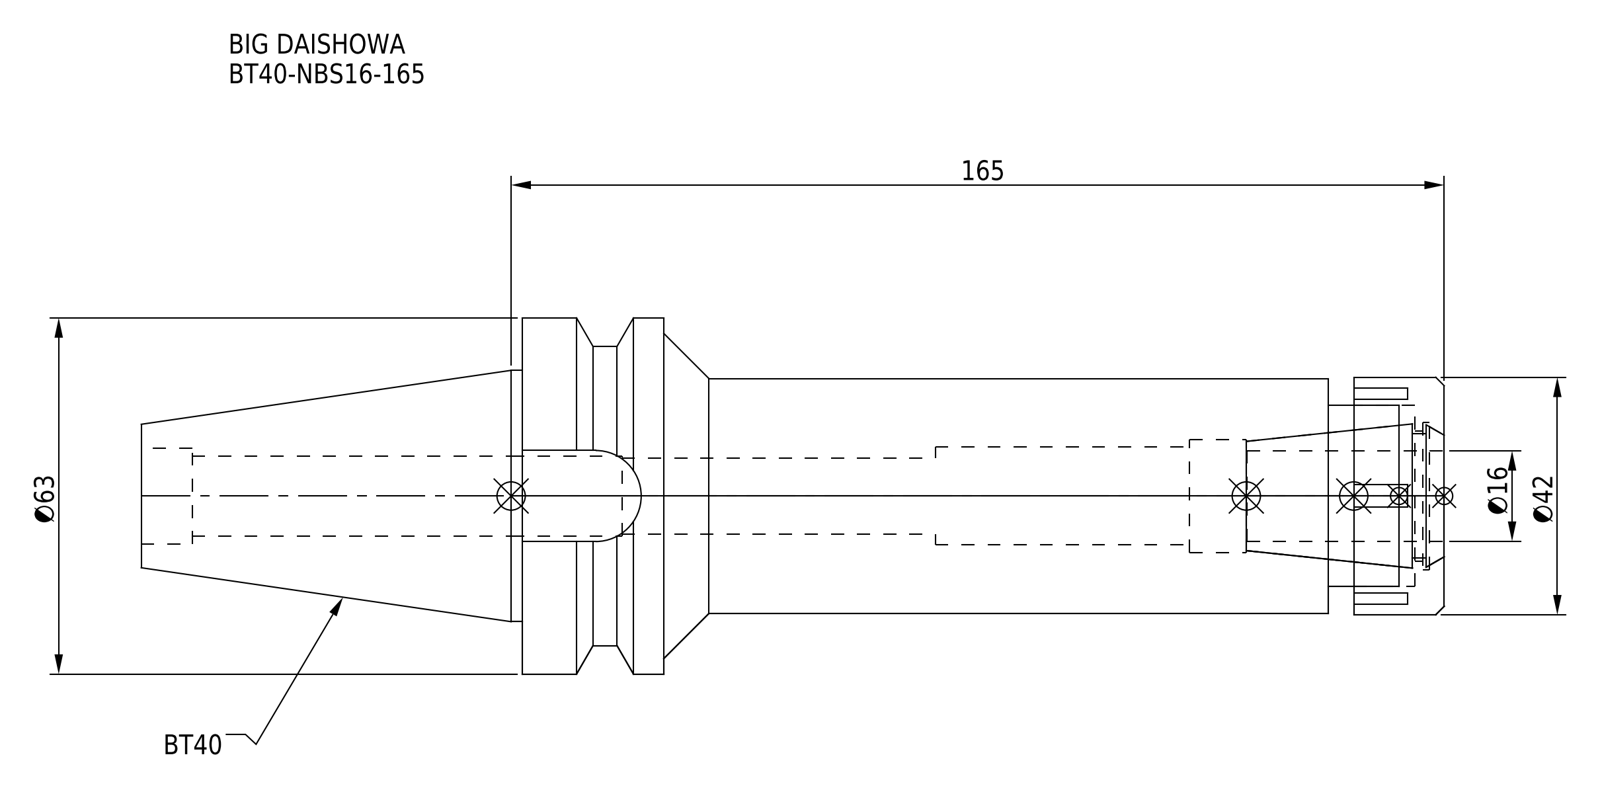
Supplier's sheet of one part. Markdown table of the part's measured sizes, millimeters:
| quantity | value |
| --- | --- |
| part name | DXF_TEMP_ASSY_ASM_4_ASM.stp; BT40-NBS16-165.stp; BT40-NBS16-165; BT40NB16165-160_ASM.stp (+3 more) |
| STEP written by | SolidWorks 2019 (CONFIG_CONTROL_DESIGN) |
| units | millimeters |
| bodies | 2 solids, 93 faces (45 planar, 34 cylindrical, 14 other) |
| overall size | 230.4 × 63 × 63 |
| volume | 272 263 mm³ |
| surface area | 51 448 mm² |
| round holes (diameter × count) | 13.5 × 1, 14.2 × 1, 17 × 1, 17.3 × 1, 20 × 1, 23 × 1, 26 × 1, 32 × 1 |
| round bosses / shafts (diameter × count) | 63 × 1, 53 × 1, 44.45 × 1, 42 × 1, 41.5 × 1 |
| partial cylindrical surfaces (radius × count) | 8.05 × 1 |
| main face-to-face distances | 163, 8, 20.5, 142.5, 16, 4.5, 147, 138, 122, 117.5 |
